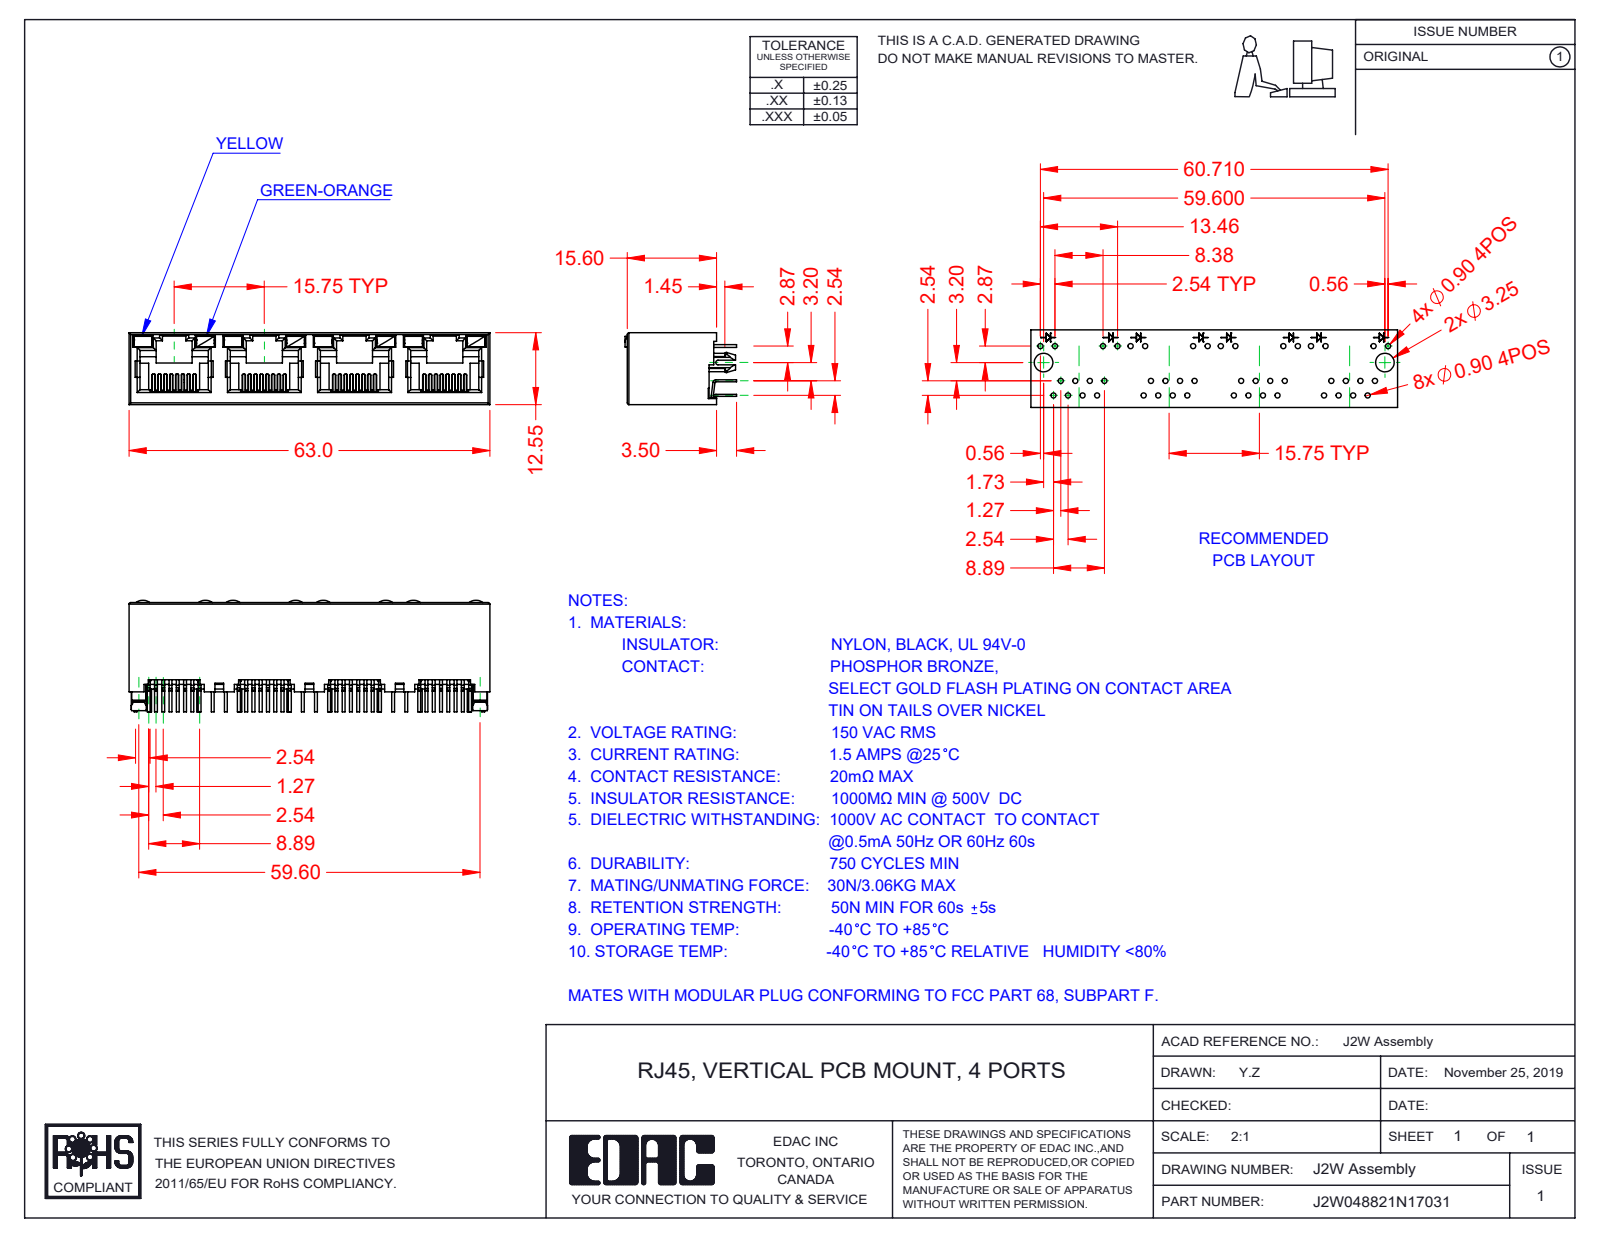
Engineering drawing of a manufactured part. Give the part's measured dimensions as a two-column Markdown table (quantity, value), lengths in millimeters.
| quantity | value |
| --- | --- |
| part name | 2W LED LH_1-Yellow; 2W LED RH_7-Green-Orange; 2W Contact Lock; 2W Contacts (+2 more) |
| STEP written by | SolidWorks 2020 (CONFIG_CONTROL_DESIGN) |
| units | millimeters |
| bodies | 45 solids, 3139 faces (2600 planar, 481 cylindrical, 58 other) |
| overall size | 63 × 19.5 × 12.55 |
| volume | 5 335 mm³ |
| surface area | 13 144 mm² |
| partial cylindrical surfaces (radius × count) | 0.15 × 64, 0.2 × 29, 0.5 × 28, 0.3 × 14, 0.45 × 8, 2 × 8, 0.25 × 2, 1.5 × 2 |
| main face-to-face distances | 12.55, 11.9, 0.65, 15.75, 0.36, 1.5, 0.78, 0.6, 11.3, 31.5 |
